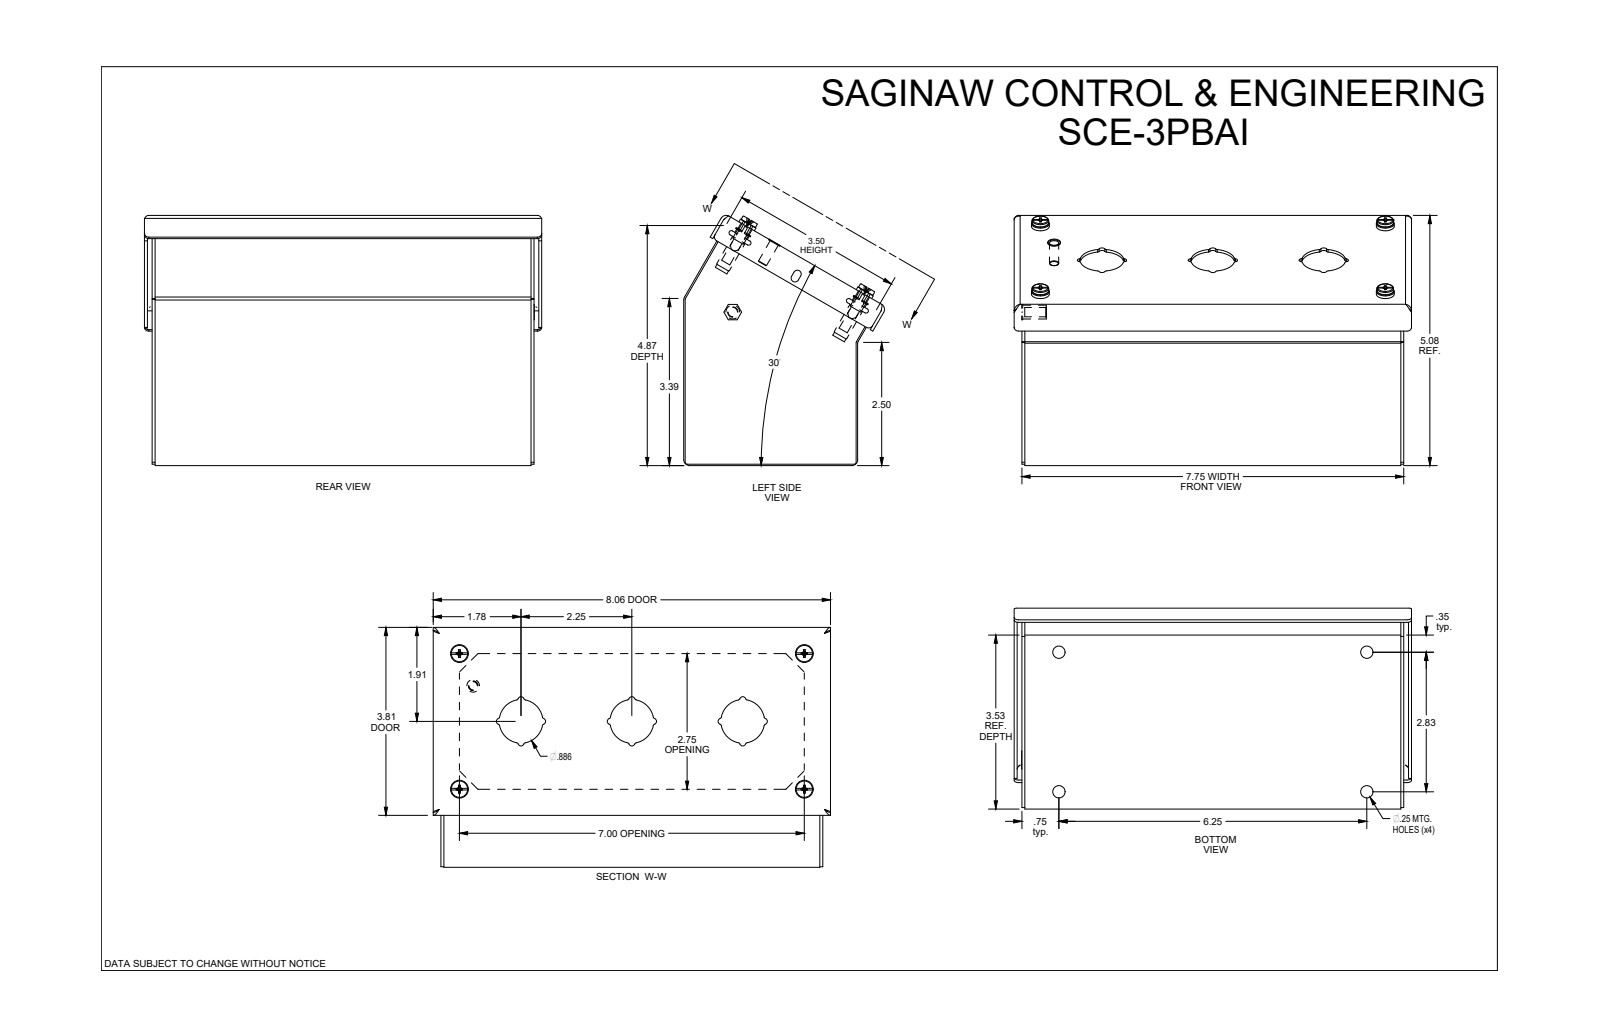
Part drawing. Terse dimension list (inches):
name: SCE-3PBAI
written by: SolidWorks 2021 (AUTOMOTIVE_DESIGN)
unit: in
bodies: 16 solids, 442 faces (164 planar, 136 cylindrical, 142 other)
size: 8.063 × 5.098 × 4.097
volume: 10.23 in³; area: 346.3 in²
holes: 5× ⌀0.19, 4× ⌀0.22, 4× ⌀0.25, 4× ⌀0.266, 4× ⌀0.317
bosses: 5× ⌀0.188, 4× ⌀0.362, 4× ⌀0.34, 4× ⌀0.334, 4× ⌀0.292, 4× ⌀0.27, 4× ⌀0.26, 4× ⌀0.146
rounds: 24× R0.04, 22× R0.06, 8× R0.062, 6× R0.12, 4× R0.063, 3× R0.443
face distances: 0.06, 0.06, 3.53, 3.47, 3.47, 3.41, 7.75, 7.69, 7.69, 7.63
hole spacings: 2.753, 7, 2.75, 7.522, 6.995, 7.005, 7.517, 7.521
